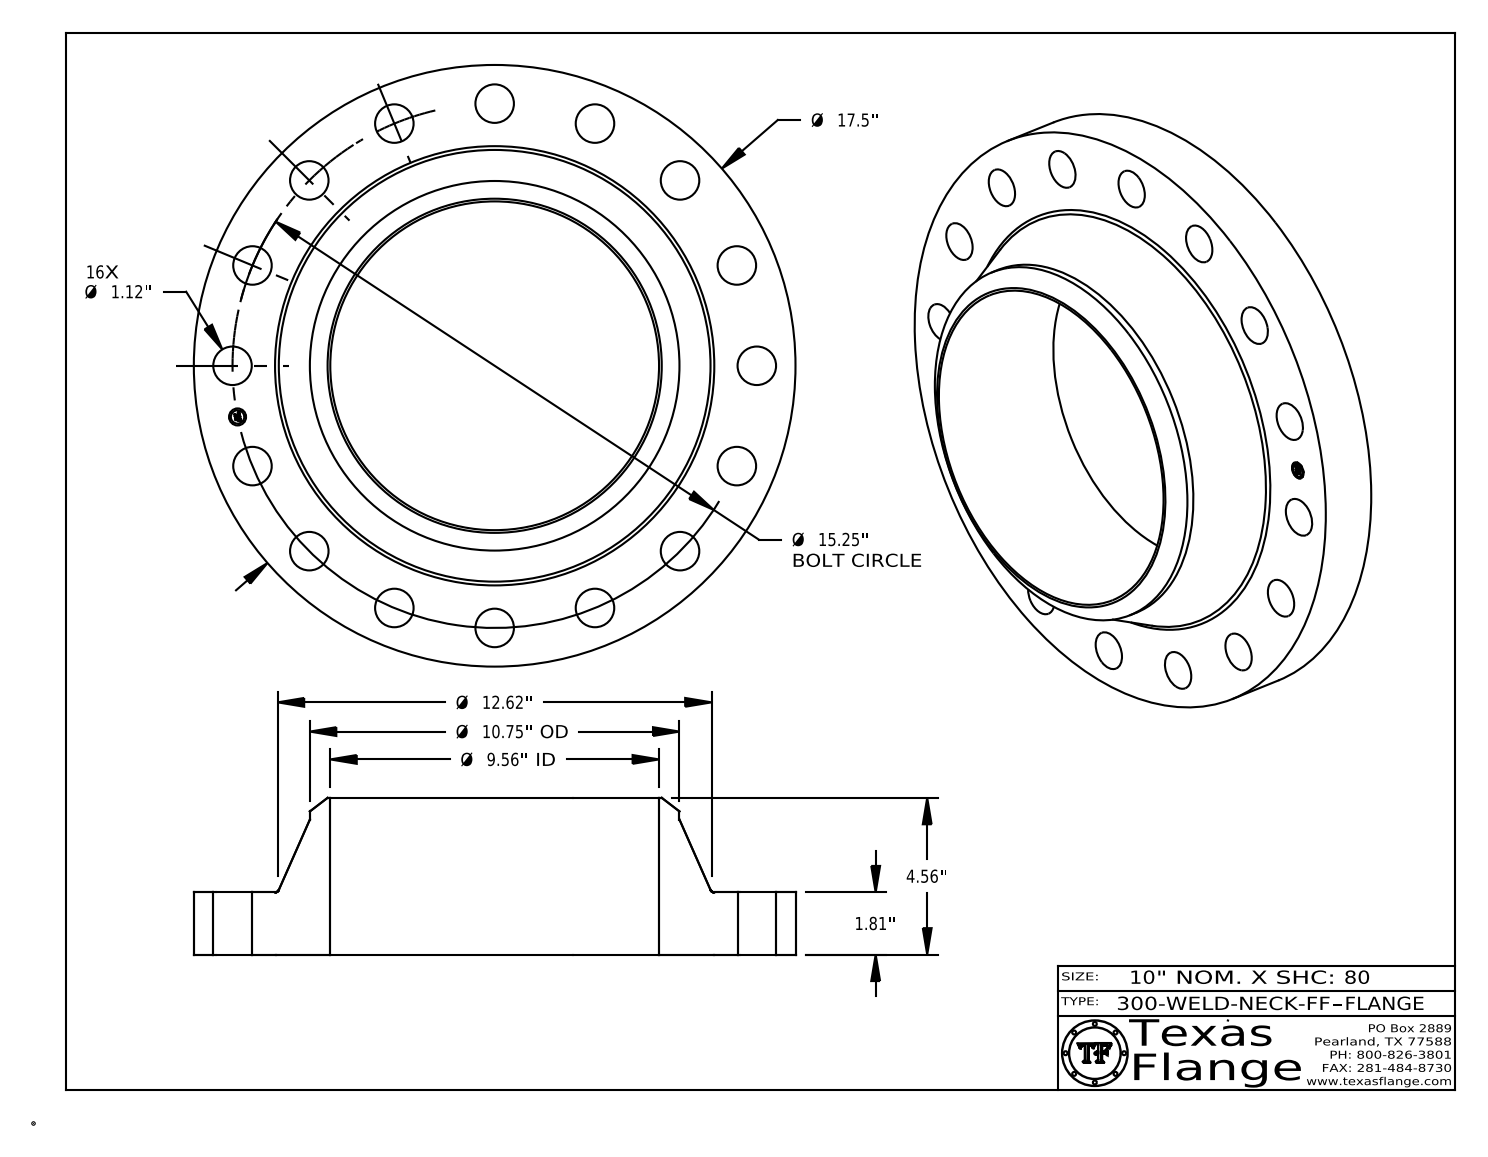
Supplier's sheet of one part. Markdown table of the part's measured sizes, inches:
| quantity | value |
| --- | --- |
| part name | 300-WELD-NECK-FF |
| STEP written by | CATIA V5 STEP AP214 (AUTOMOTIVE_DESIGN) |
| units | inches |
| bodies | 1 solid, 433 faces (369 planar, 58 cylindrical, 6 other) |
| overall size | 17.5 × 17.5 × 4.56 |
| volume | 361.1 in³ |
| surface area | 706.7 in² |
| round holes (diameter × count) | 1.12 × 16, 0.495 × 1, 9.562 × 1 |
| round bosses / shafts (diameter × count) | 0.03 × 8, 17.5 × 1, 10.75 × 1, 0.39 × 1 |
| main face-to-face distances | 1.81, 4.56, 2.75, 0.015, 1.795, 2.765, 0.148, 0.145, 0.027, 0.096 |
| hole center spacings | 8.472, 10.783, 14.957, 14.089, 7.625, 2.975, 2.975, 5.836 |
